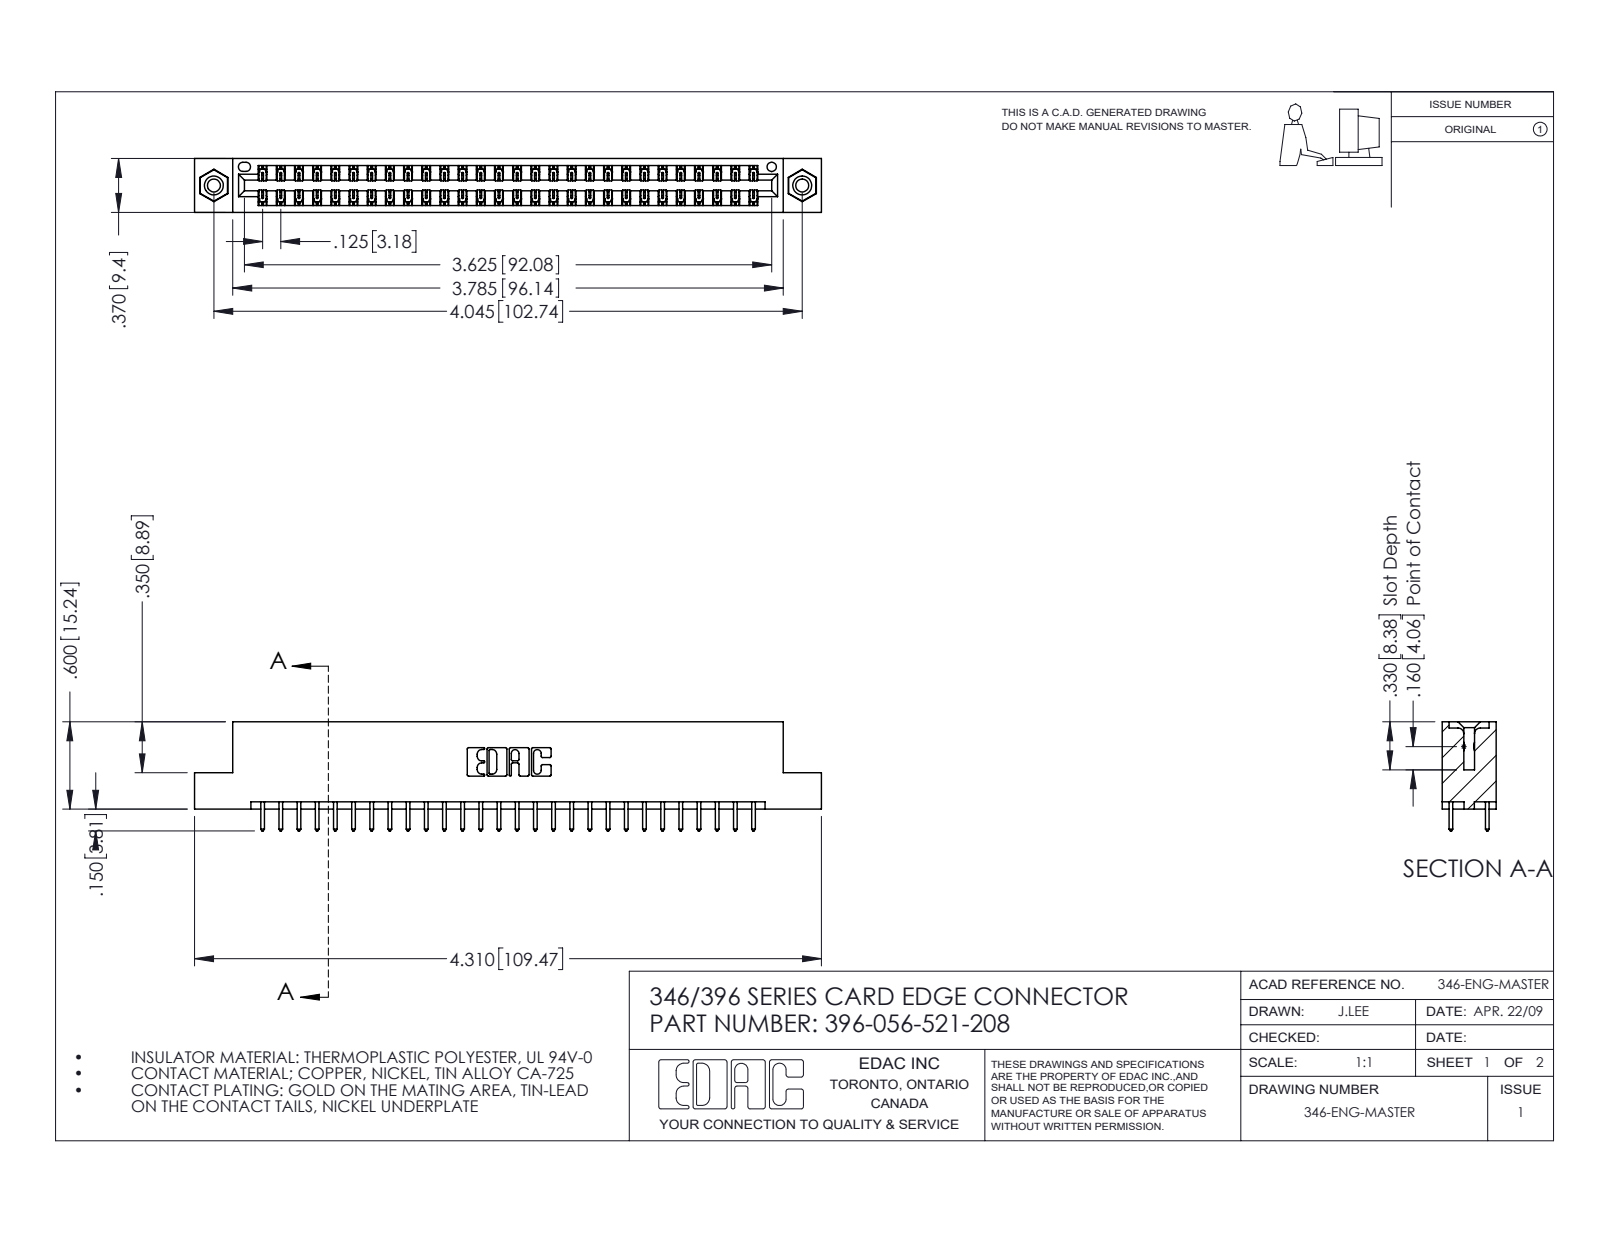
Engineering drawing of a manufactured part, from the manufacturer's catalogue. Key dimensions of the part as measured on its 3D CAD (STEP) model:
Part name (STEP PRODUCT): 396-056-521-208; 346 Part_Flush Mounting Lugs - 0.156 Dia-TI; 345-292-001_345-293-121; 345-250-001_345-250-003-102
STEP written by: SolidWorks 2016 (CONFIG_CONTROL_DESIGN)
Units: inches
Bodies: 59 solids, 3094 faces (2068 planar, 1010 cylindrical, 16 other)
Overall size (bounding box): 4.31 × 0.75 × 0.37
Volume: 0.643 in³ · Surface area: 21.9 in²
Round holes (diameter × count): ⌀0.089 ×2, ⌀0.125 ×2, ⌀0.156 ×2, ⌀0.064 ×1
Round bosses / shafts (diameter × count): ⌀0.155 ×2
Partial cylindrical surfaces — rounded edges, fillets, slot ends (radius × count): R0.006 ×84, R0.01 ×56, R0.01 ×22, R0.007 ×6, R0.031 ×6, R0.026 ×3, R0.014 ×2, R0.022 ×2
Main face-to-face distances: 0.048, 0.322, 0.25, 0.37, 0.072, 0.298, 0.025, 0.275, 0.148, 0.222
Hole centre spacings: 0.246, 3.837, 4.045
